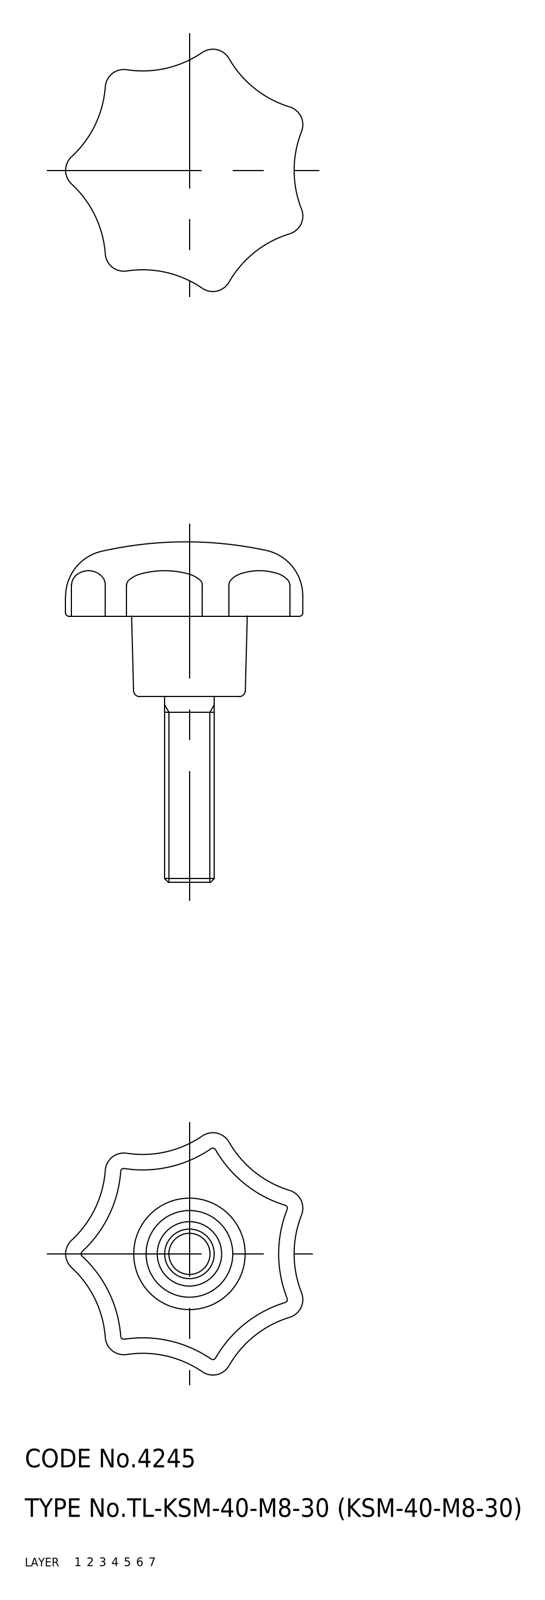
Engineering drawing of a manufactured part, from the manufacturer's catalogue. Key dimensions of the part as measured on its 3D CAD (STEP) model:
Part name (STEP PRODUCT): screw; knob; KSM_40_M8_30_9218_36
STEP written by: CADfix (AUTOMOTIVE_DESIGN)
Units: millimetres
Bodies: 2 solids, 103 faces (0 planar, 0 cylindrical, 103 other)
Overall size (bounding box): 55 × 39.15 × 38.32
Volume: 12 012 mm³ · Surface area: 6 707 mm²
